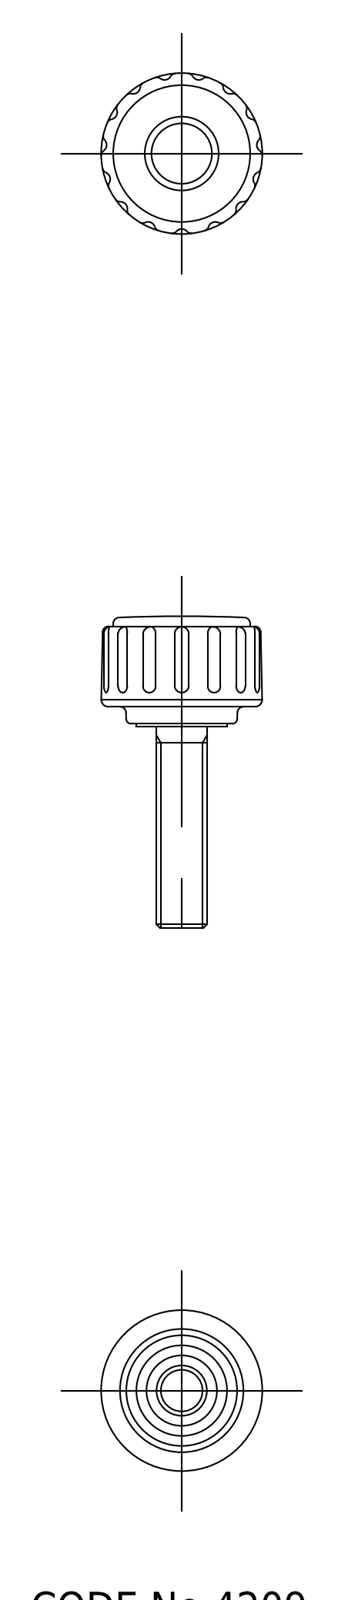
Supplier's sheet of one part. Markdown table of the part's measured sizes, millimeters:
| quantity | value |
| --- | --- |
| part name | screw; knob; KDM_16_M5_20_2406_36 |
| STEP written by | CADfix (AUTOMOTIVE_DESIGN) |
| units | millimeters |
| bodies | 2 solids, 68 faces (0 planar, 0 cylindrical, 68 other) |
| overall size | 30.95 × 16.12 × 15.97 |
| volume | 1 629 mm³ |
| surface area | 1 474 mm² |
